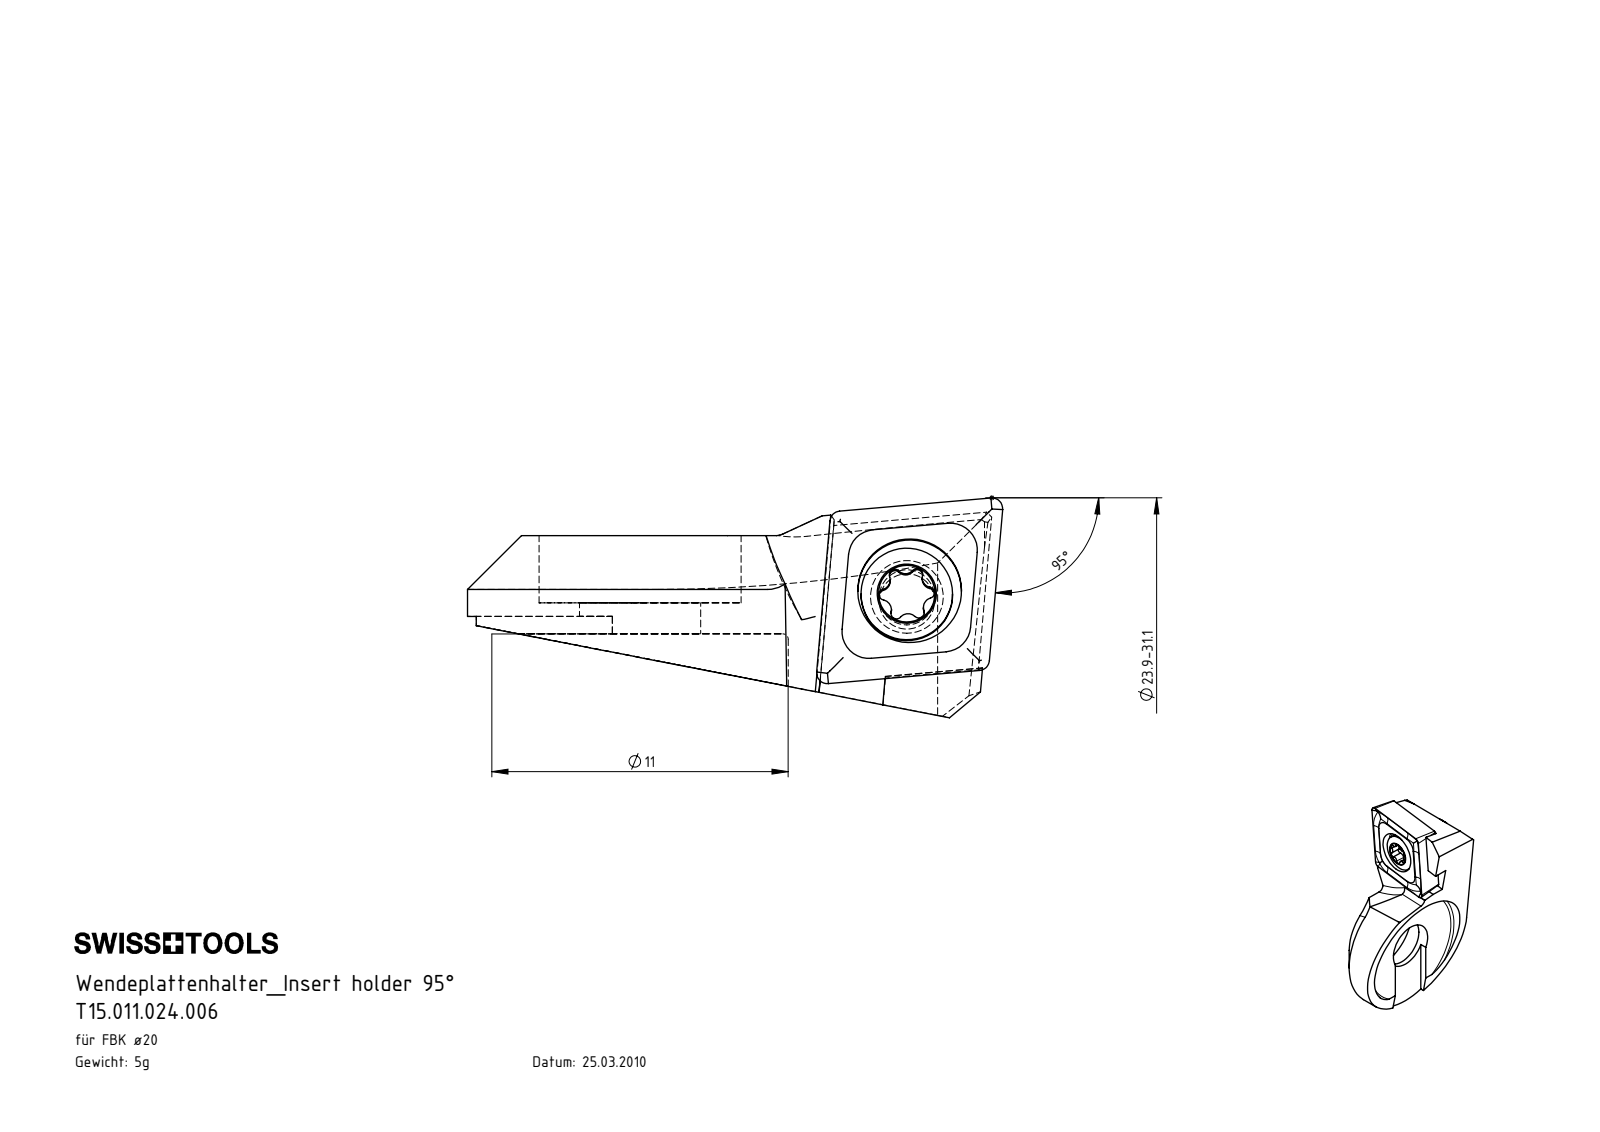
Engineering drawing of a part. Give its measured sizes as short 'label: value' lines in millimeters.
name: F20.WCA.002.005; WCA-ER2.001.006_A; CCMT060204; F20-WCA.002.005_E_fertigbearbeitet
written by: SolidWorks 2017 (AUTOMOTIVE_DESIGN)
unit: mm
bodies: 3 solids, 104 faces (40 planar, 27 cylindrical, 37 other)
size: 19.86 × 12.8 × 8.16
volume: 549 mm³; area: 848 mm²
holes: 1× ⌀2.05, 1× ⌀2.8, 1× ⌀3.85, 1× ⌀4.5, 1× ⌀7.5
bosses: 1× ⌀3.4, 1× ⌀2.5
rounds: 6× R0.21, 5× R0.36, 2× R0.5, 2× R5, 1× R0.36, 1× R5.5, 1× R6.4, 1× R10
face distances: 1.15, 2.5, 3.65, 3, 0.5, 0.65, 2.38, 1.08, 1.3, 0.98
